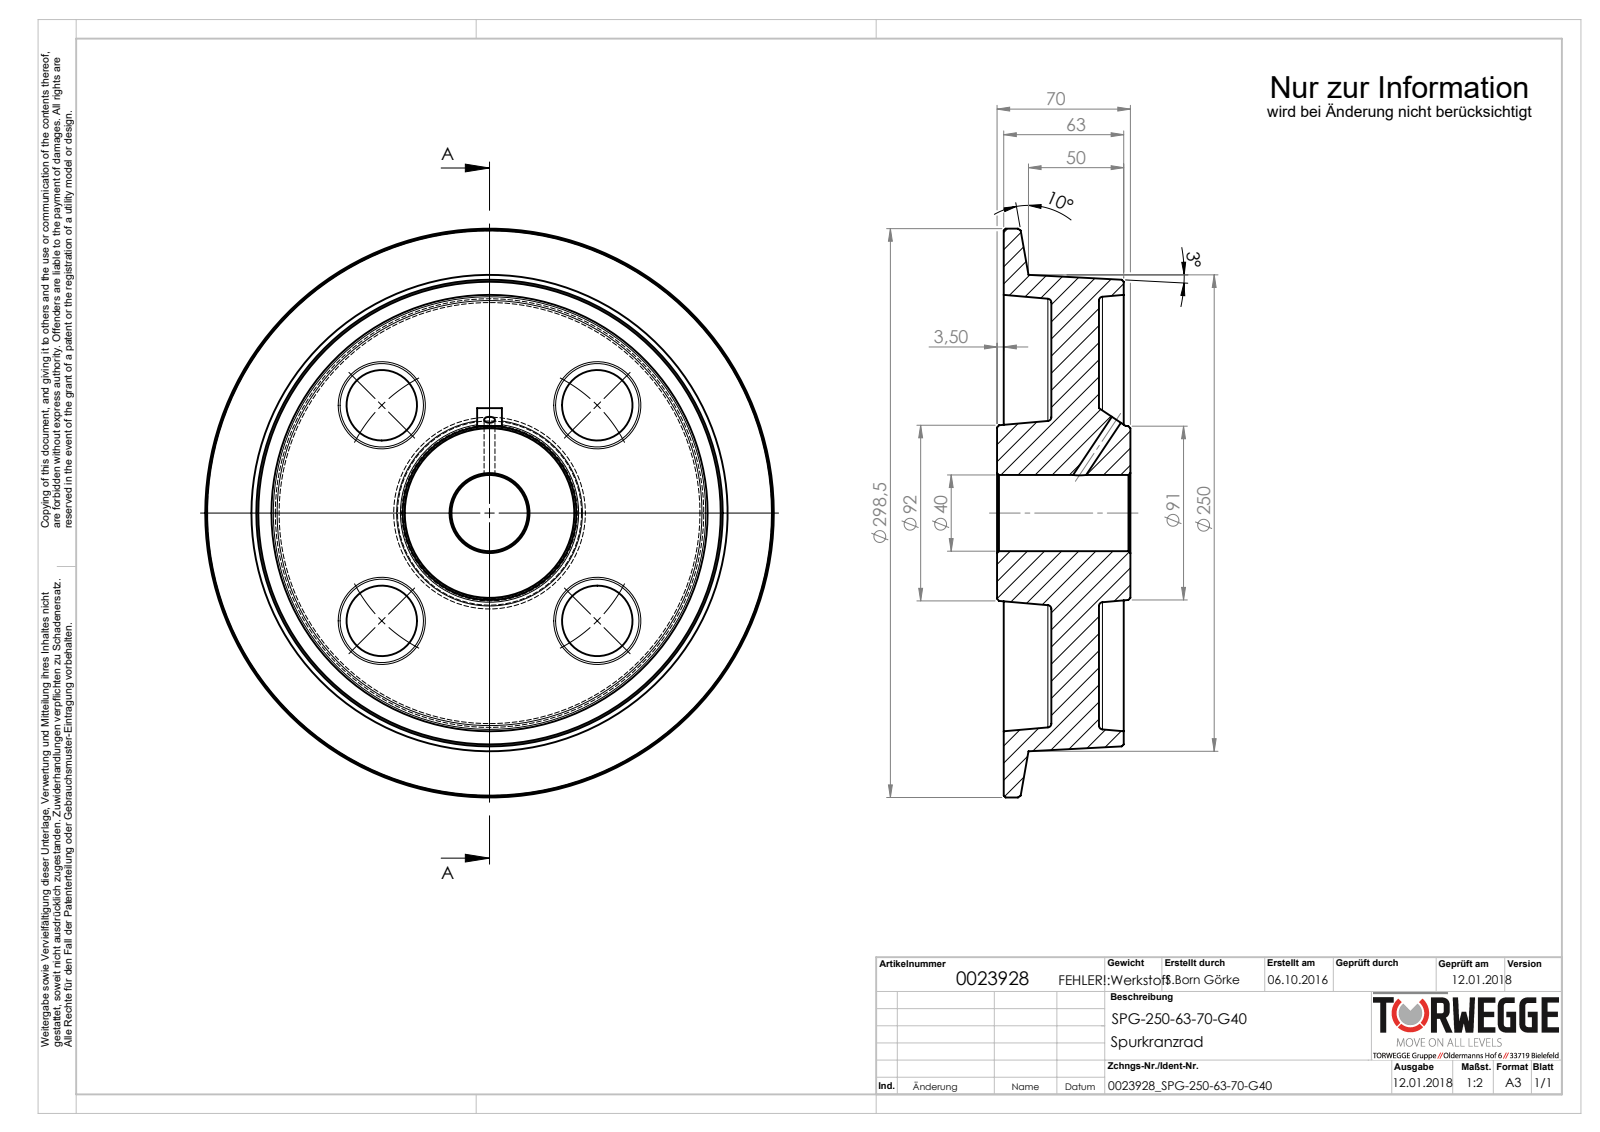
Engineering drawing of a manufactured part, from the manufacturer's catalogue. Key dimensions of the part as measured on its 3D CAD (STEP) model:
Part name (STEP PRODUCT): 0023928_SPG-250-63-70-G40
STEP written by: SolidWorks 2016 (AUTOMOTIVE_DESIGN)
Units: millimetres
Bodies: 0 solids, 42 faces (10 planar, 3 cylindrical, 29 other)
Overall size (bounding box): 298.5 × 298.5 × 70.28
Round holes (diameter × count): ⌀40 ×1
Round bosses / shafts (diameter × count): ⌀298.5 ×1, ⌀8 ×1
Main face-to-face distances: 25, 50, 3.5, 66.5, 13, 63, 38, 28.5, 53.5, 70
